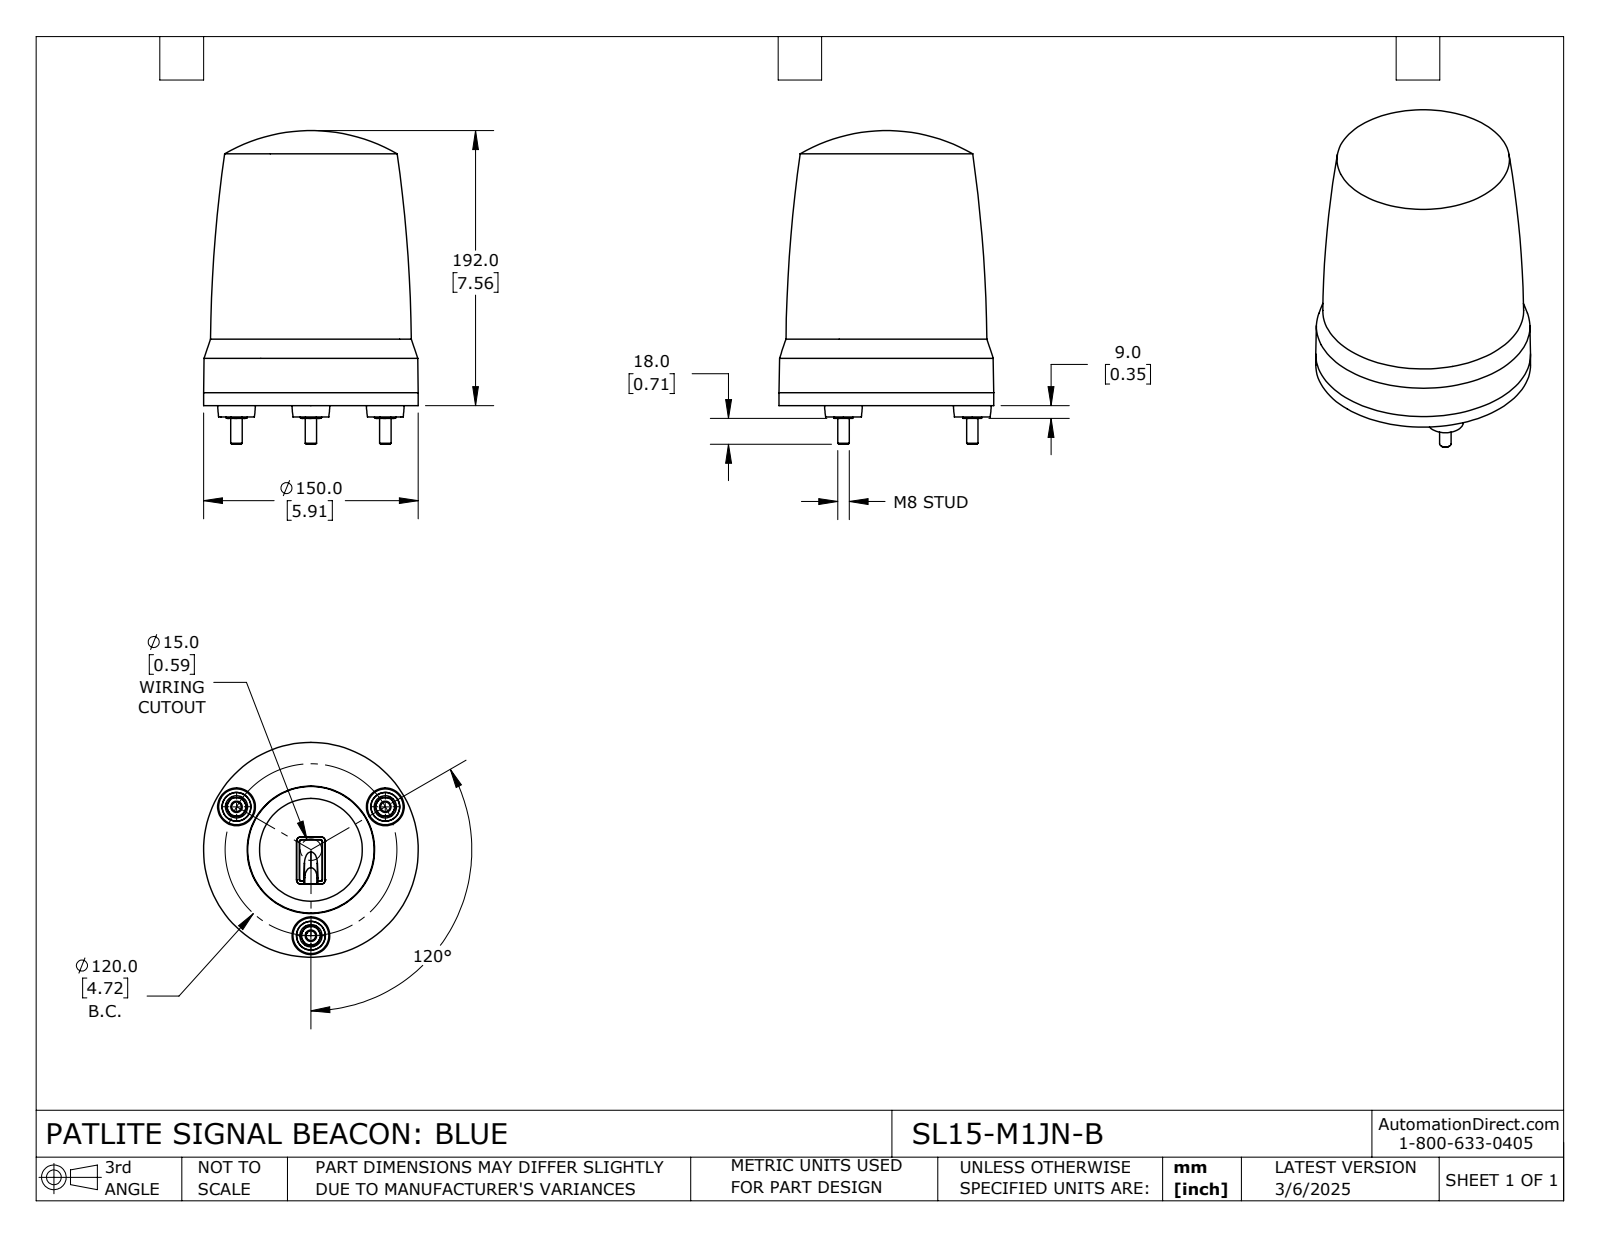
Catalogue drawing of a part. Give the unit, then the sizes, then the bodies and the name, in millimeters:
Units: millimetres
Overall size (bounding box): 219 × 150 × 150
Round bosses / shafts (diameter × count): ⌀15.5 ×3, ⌀8 ×3, ⌀150 ×1
Main face-to-face distances: 32.7, 8, 40.7, 13, 7.1, 0.9, 33.6, 1.6, 36.05, 41.55
Volume: 2 538 000 mm³ · Surface area: 119 026 mm²
Bodies: 1 solid, 144 faces (49 planar, 14 cylindrical, 81 other)
Part name (STEP PRODUCT): SL15-M1JN-B
STEP written by: SolidWorks 2024 (CONFIG_CONTROL_DESIGN)
